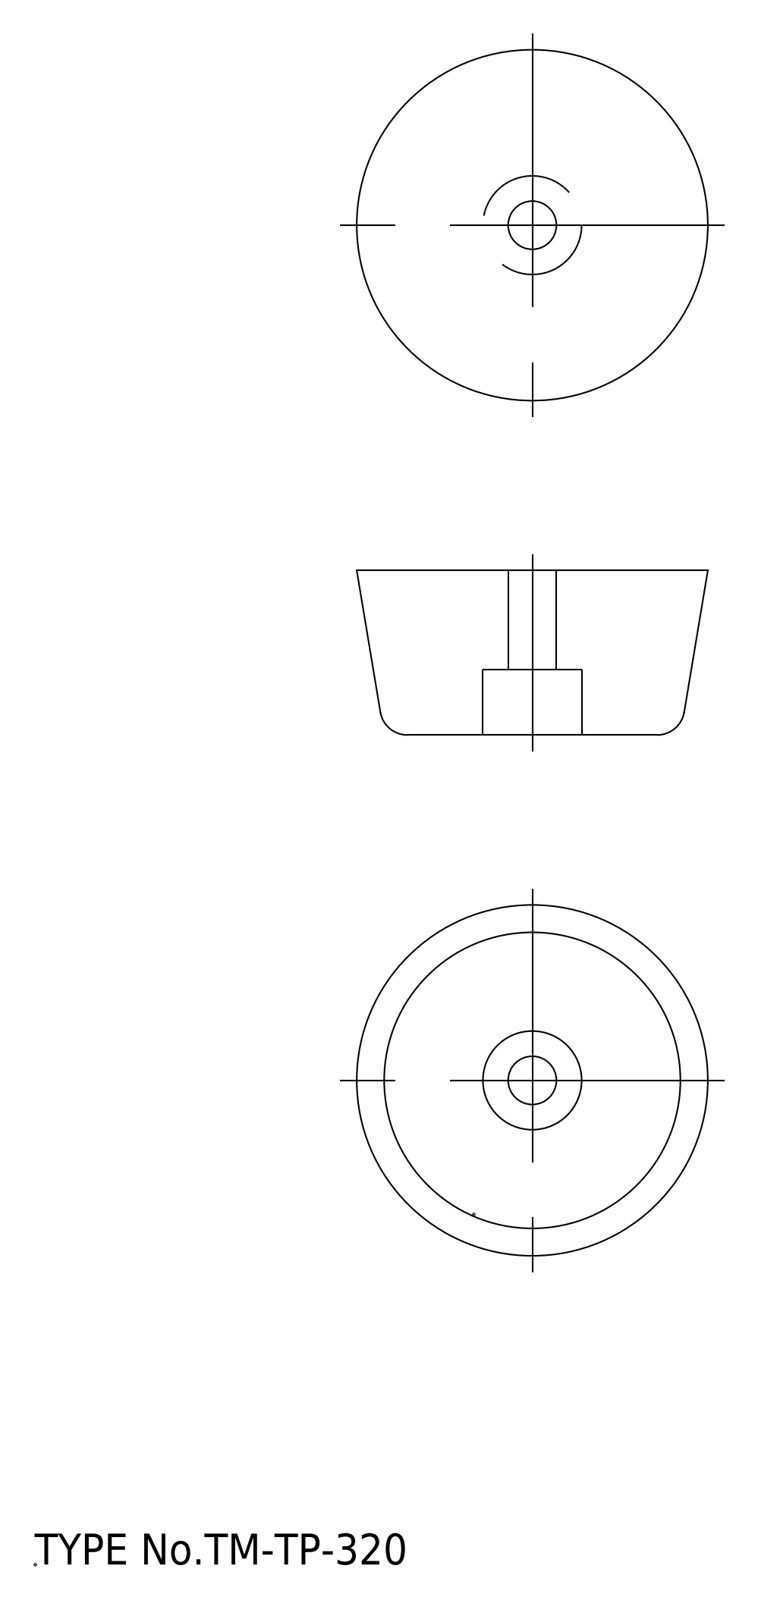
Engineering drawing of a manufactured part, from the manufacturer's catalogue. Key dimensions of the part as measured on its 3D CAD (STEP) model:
STEP written by: spGate 19.8.4 (****-****-****-****) (AUTOMOTIVE_DESIGN)
Units: millimetres
Bodies: 1 solid, 11 faces (3 planar, 4 cylindrical, 4 other)
Overall size (bounding box): 32 × 32 × 15
Volume: 9 703 mm³ · Surface area: 2 989 mm²
Round holes (diameter × count): ⌀4.4 ×1, ⌀9 ×1
Main face-to-face distances: 15, 6, 9
